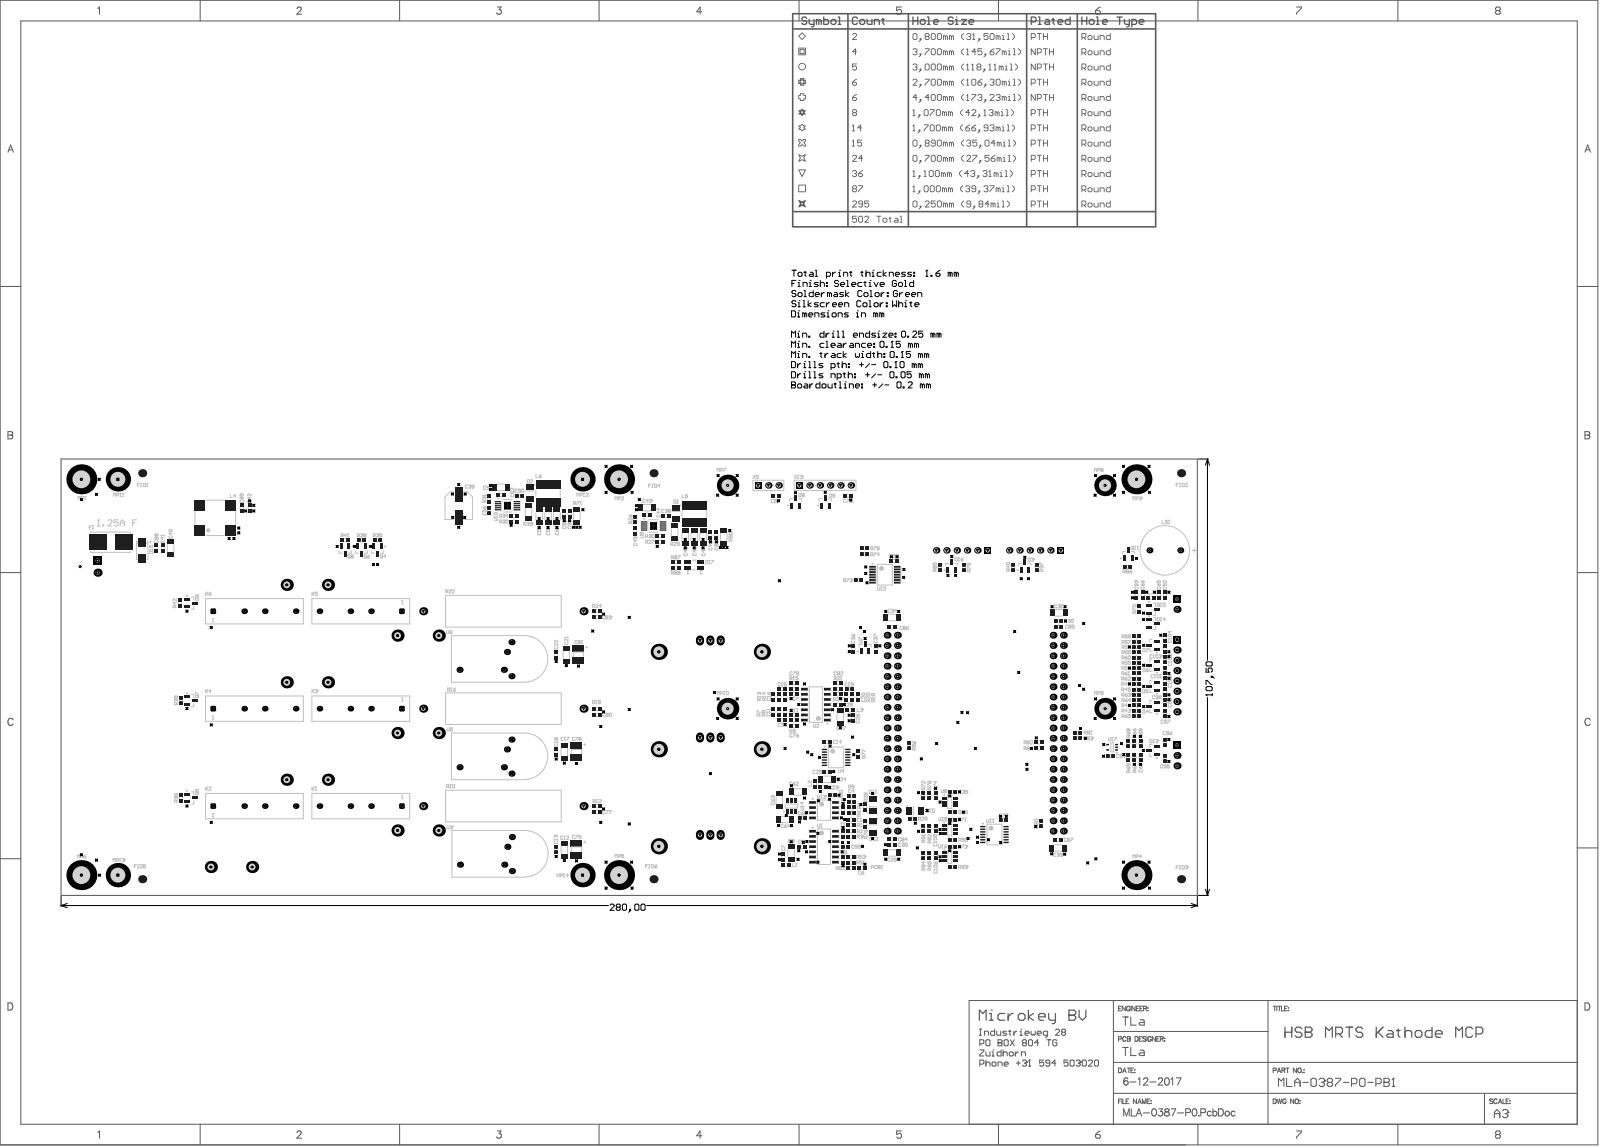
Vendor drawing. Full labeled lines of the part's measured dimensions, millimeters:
Part name (STEP PRODUCT): PCB; Board; MP14; 9774080151 (+8 more)
STEP written by: Open CASCADE 6.8 (AUTOMOTIVE_DESIGN)
Units: millimetres
Bodies: 584 solids, 15010 faces (10464 planar, 2173 cylindrical, 2373 other)
Overall size (bounding box): 280 × 107.5 × 53.19
Volume: 110 579 mm³ · Surface area: 124 366 mm²
Round holes (diameter × count): ⌀1 ×87, ⌀1.1 ×36, ⌀0.7 ×25, ⌀0.89 ×15, ⌀1.7 ×14, ⌀1.07 ×8, ⌀2.3 ×6, ⌀2.46 ×6, ⌀2.7 ×6, ⌀4.4 ×6, ⌀3 ×5, ⌀1.57 ×4
Round bosses / shafts (diameter × count): ⌀1.8 ×14, ⌀6 ×6, ⌀4.2 ×6, ⌀0.85 ×6, ⌀5.1 ×4, ⌀4.35 ×4, ⌀3.5 ×4, ⌀2.8 ×4
Partial cylindrical surfaces — rounded edges, fillets, slot ends (radius × count): R0.1 ×388, R0.13 ×117, R0.2 ×74, R0.3 ×18, R0.3 ×12, R0.75 ×12, R0.5 ×11, R0.15 ×8
Main face-to-face distances: 1.85, 10.39, 12.24, 11.99, 1.6, 13.84, 1.5, 24, 22.75, 5.75
Hole centre spacings: 24, 7.62, 10.16, 12.7, 26.18, 20.32, 28.49, 2.45
